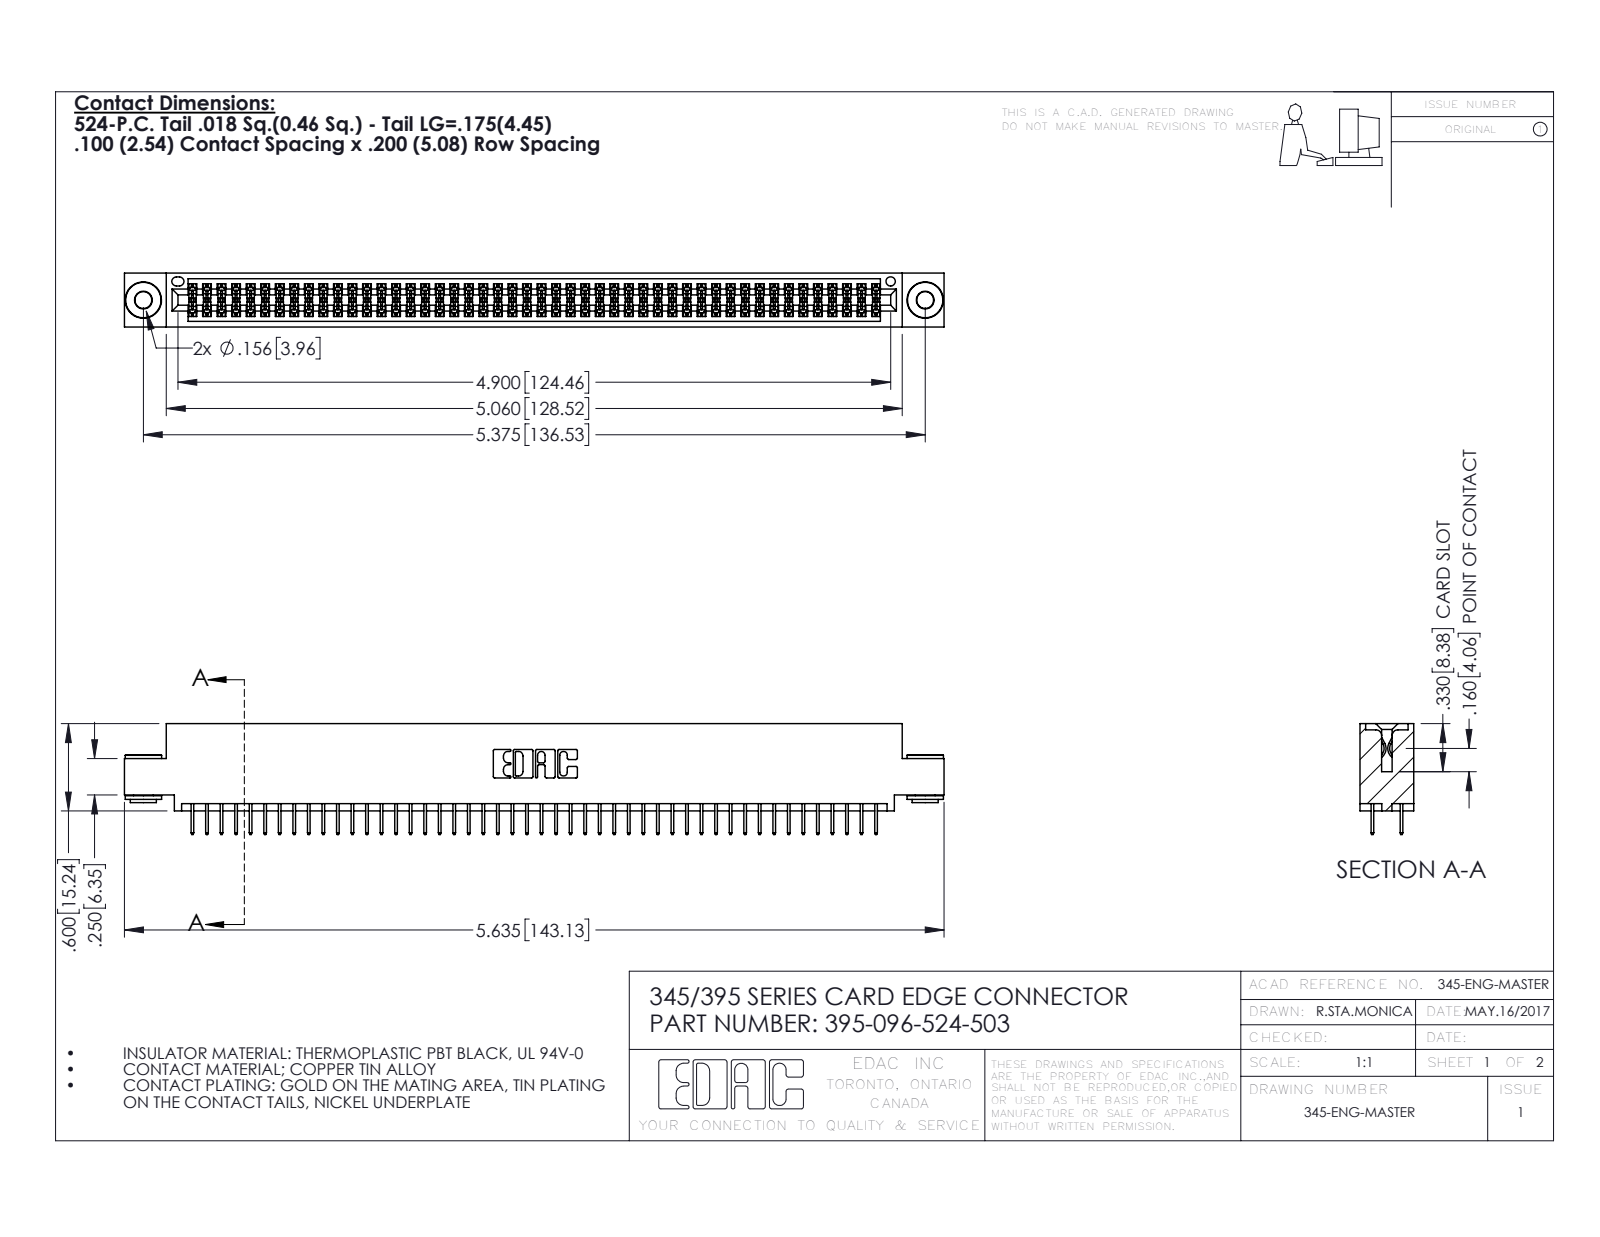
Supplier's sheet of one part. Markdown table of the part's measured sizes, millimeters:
| quantity | value |
| --- | --- |
| part name | 345 Part_0.110 Offset - 0.156 Dia-TH; 345-250-002_345-250-002-102; 345-292-001_345-293-124; 395-096-524-503 |
| STEP written by | SolidWorks 2016 (CONFIG_CONTROL_DESIGN) |
| units | millimeters |
| bodies | 99 solids, 5352 faces (3838 planar, 1506 cylindrical, 8 other) |
| overall size | 143.1 × 19.4 × 9.4 |
| volume | 13 800 mm³ |
| surface area | 20 370 mm² |
| round holes (diameter × count) | 2.9 × 2, 4 × 2, 1.6 × 1 |
| round bosses / shafts (diameter × count) | 6.4 × 2, 4.6 × 2, 3.5 × 2 |
| partial cylindrical surfaces (radius × count) | 0.2 × 144, 0.3 × 22, 0.2 × 6, 0.8 × 6, 0.7 × 3, 0.4 × 2, 0.5 × 2, 0.6 × 2 |
| main face-to-face distances | 1.8, 7.6, 5.1, 9.4, 0.6, 2.5, 6.9, 5.7, 1.8, 4.4 |
| hole center spacings | 6.9, 130.5, 136.5 |
